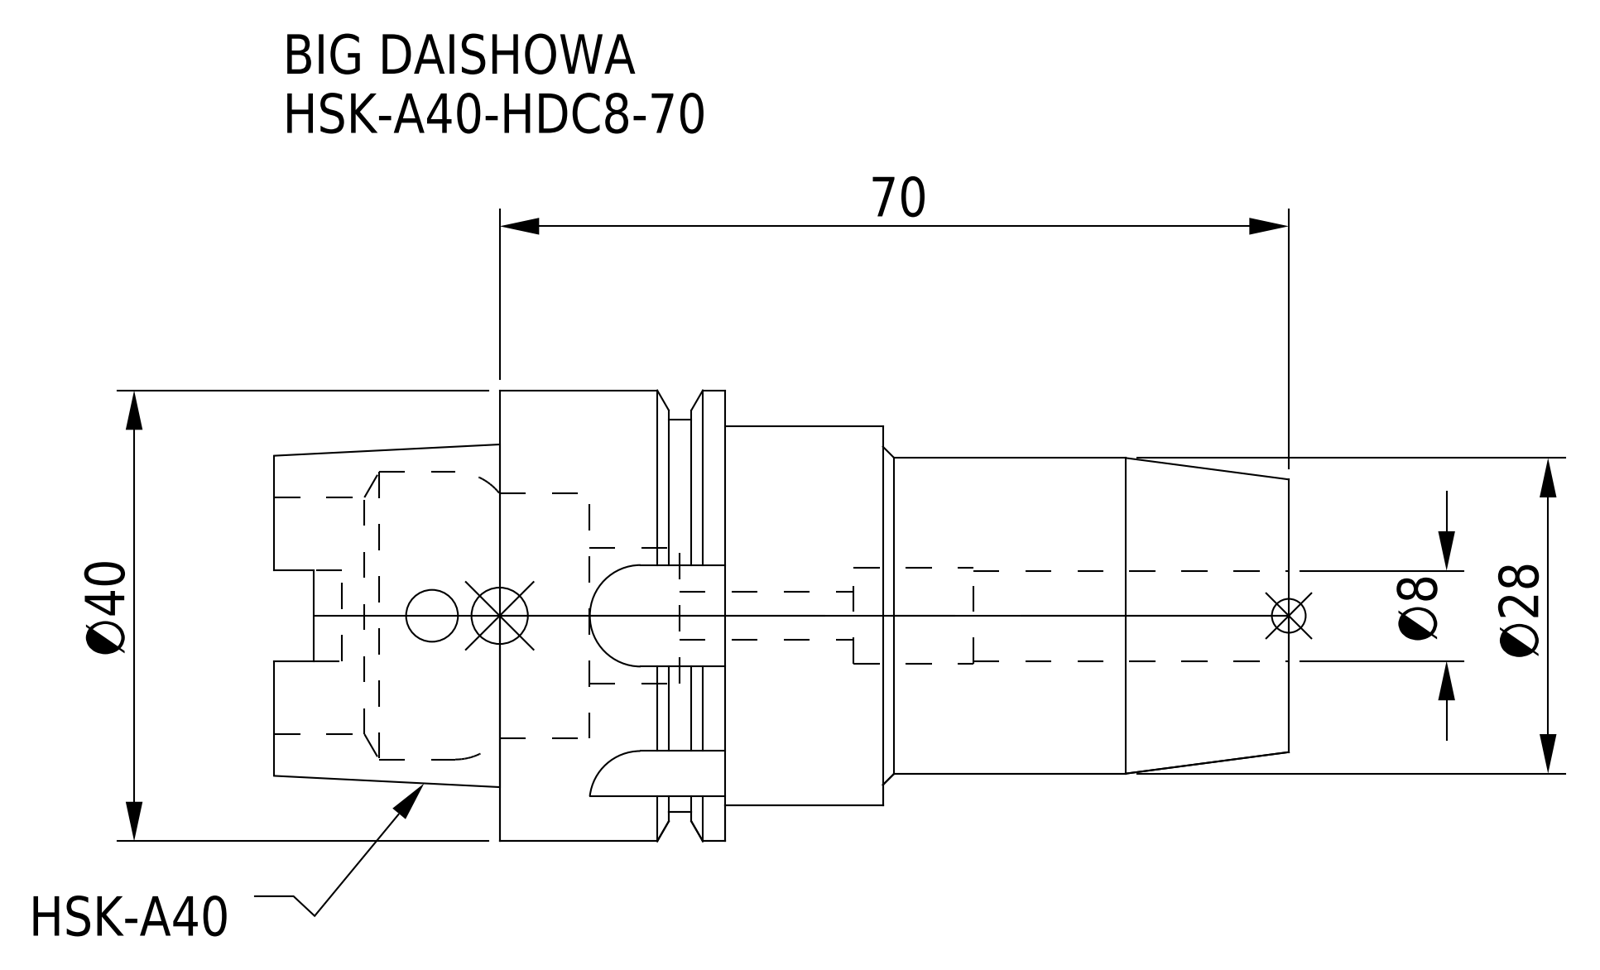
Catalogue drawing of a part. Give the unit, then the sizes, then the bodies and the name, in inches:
Units: inches
Overall size (bounding box): 3.543 × 1.575 × 1.575
Round holes (diameter × count): ⌀0.165 ×1, ⌀0.181 ×1, ⌀0.315 ×1, ⌀0.335 ×1, ⌀0.472 ×1, ⌀0.827 ×1, ⌀0.858 ×1, ⌀1.004 ×1
Round bosses / shafts (diameter × count): ⌀1.575 ×1, ⌀1.37 ×1, ⌀1.323 ×1, ⌀1.102 ×1
Partial cylindrical surfaces — rounded edges, fillets, slot ends (radius × count): R0.074 ×4, R0.177 ×4
Main face-to-face distances: 0.787, 2.756, 1.339, 1.969, 0.313, 2.443, 0.474, 0.551, 1.026, 1.417
Volume: 3.398 in³ · Surface area: 23.33 in²
Bodies: 1 solid, 97 faces (39 planar, 40 cylindrical, 18 other)
Part name (STEP PRODUCT): HSK-A40-HDC8-70
STEP written by: CREO PARAMETRIC BY PTC INC, 2016380 (AUTOMOTIVE_DESIGN)
